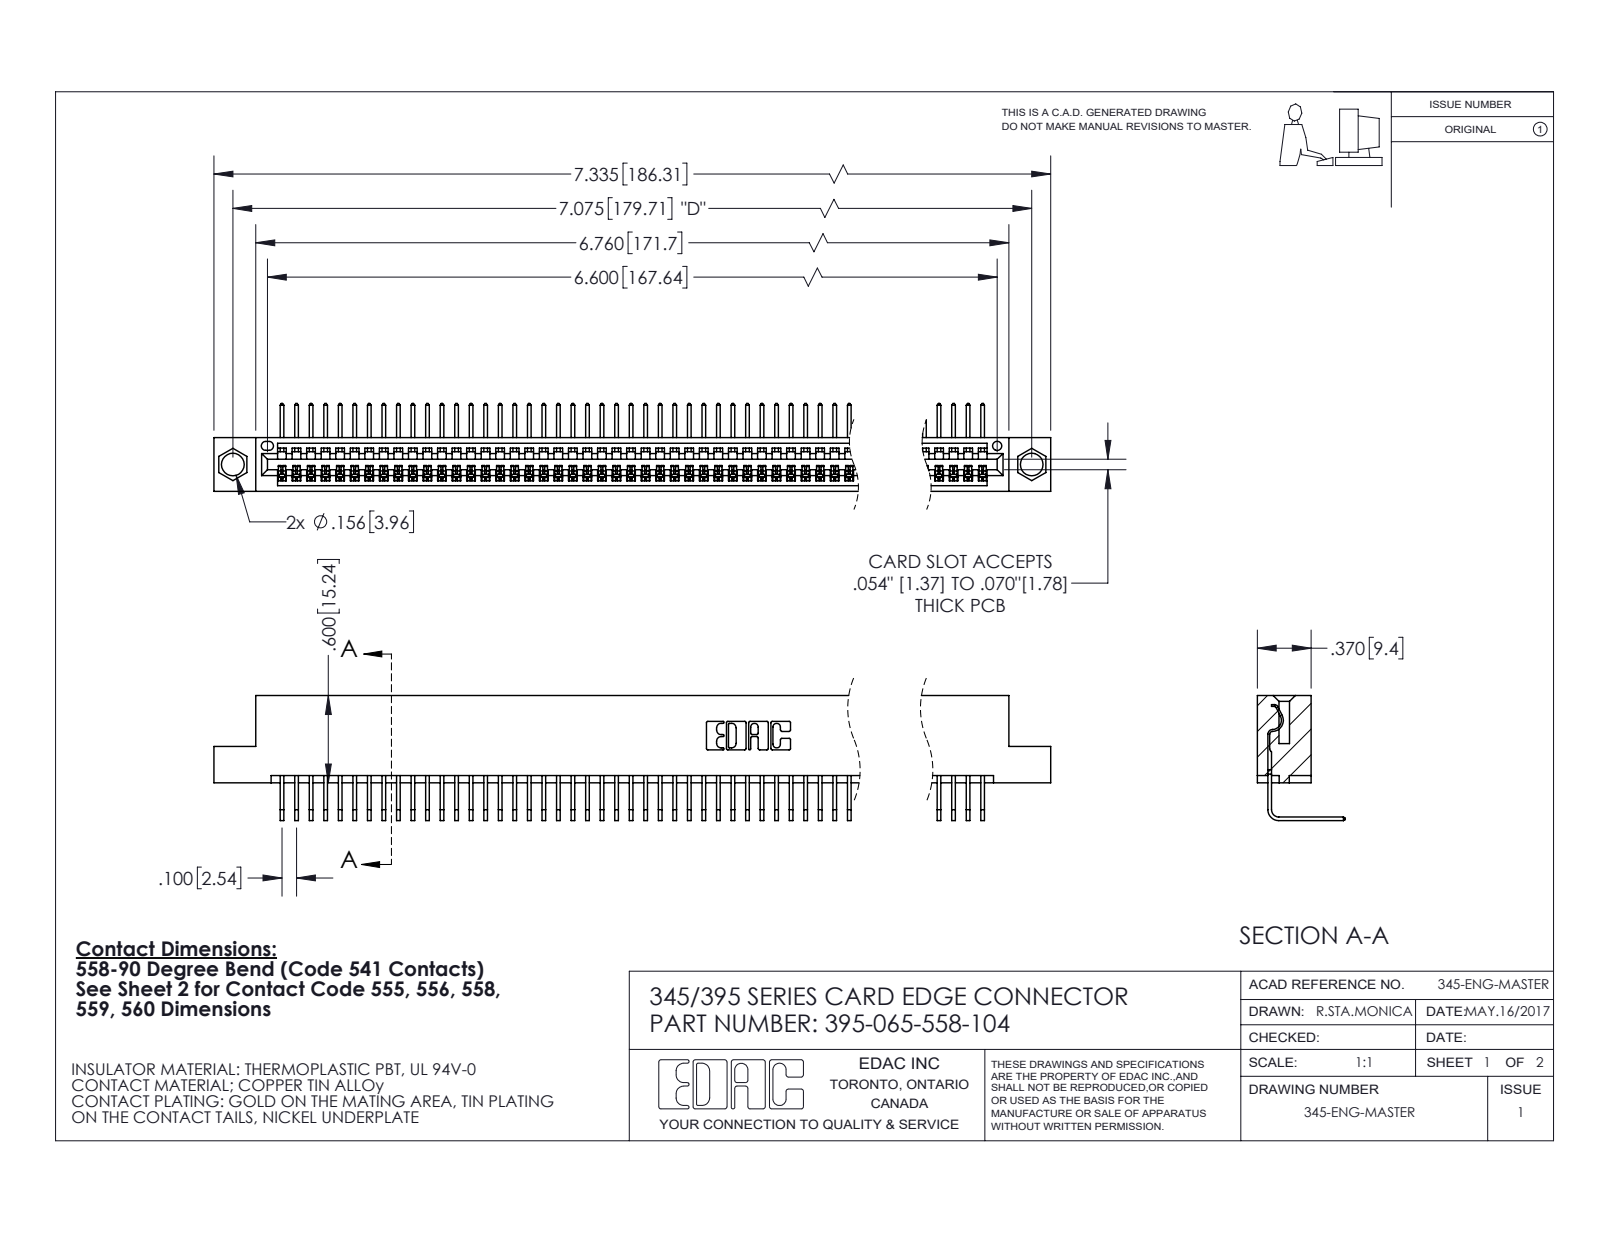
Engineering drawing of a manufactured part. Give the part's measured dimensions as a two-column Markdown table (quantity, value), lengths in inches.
| quantity | value |
| --- | --- |
| part name | 345 Part_Flush Mounting Lugs - 0.156 Dia-TI; 345-292-001_558 Tail - 2; 395-065-558-104 |
| STEP written by | SolidWorks 2020 (CONFIG_CONTROL_DESIGN) |
| units | inches |
| bodies | 66 solids, 4040 faces (2824 planar, 1216 cylindrical, 0 other) |
| overall size | 7.335 × 0.859 × 0.605 |
| volume | 1.098 in³ |
| surface area | 39.28 in² |
| round holes (diameter × count) | 0.156 × 2, 0.064 × 1 |
| partial cylindrical surfaces (radius × count) | 0.006 × 130, 0.01 × 22, 0.007 × 6, 0.031 × 6, 0.026 × 3, 0.031 × 2, 0.04 × 2, 0.014 × 1 |
| main face-to-face distances | 0.072, 0.298, 0.37, 0.2, 0.098, 0.272, 0.025, 0.225, 0.149, 0.072 |
| hole center spacings | 0.27, 6.839, 7.075 |
